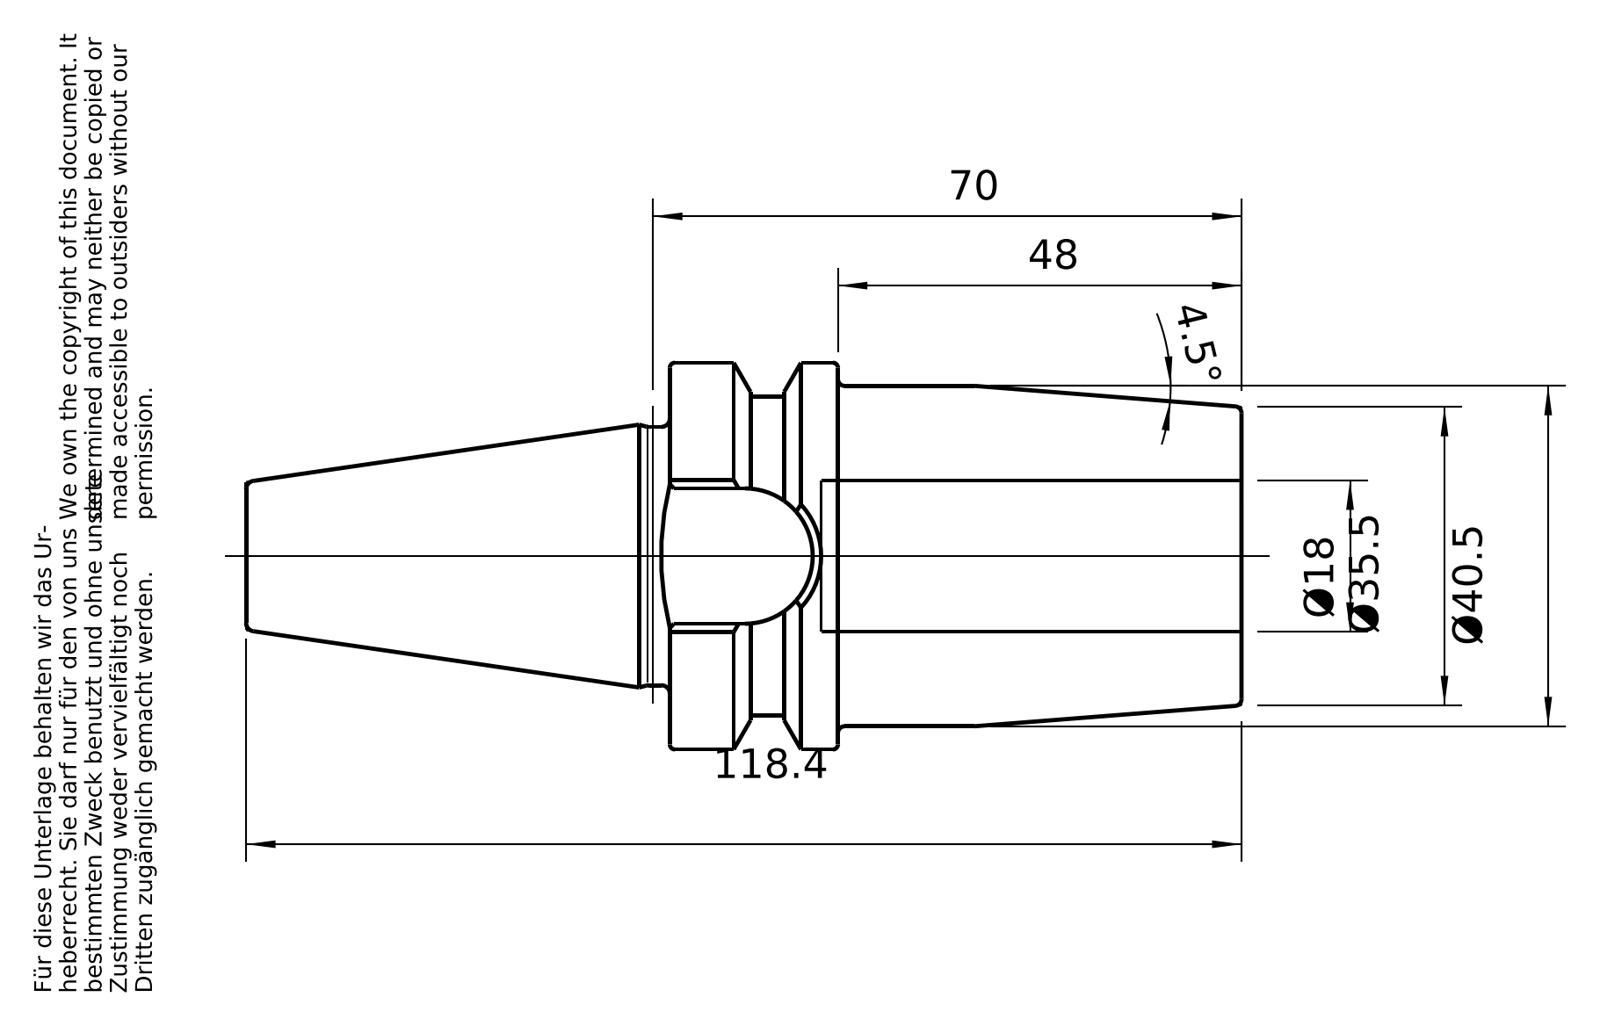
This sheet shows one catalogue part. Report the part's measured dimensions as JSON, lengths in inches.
{"part_name": "30-645-18", "step_written_by": "PRO/ENGINEER BY PARAMETRIC TECHNOLOGY CORPORATION, 2010430 (CONFIG_CONTROL_DESIGN)", "units": "inches", "bodies": {"solids": 1, "faces": 96, "planar": 26, "cylindrical": 22, "other": 48}, "overall_size": [4.661, 1.81, 1.81], "volume_in3": 5.723, "surface_area_in2": 31.25, "round_holes": [[0.398, 1], [0.493, 1], [0.512, 1], [0.709, 1]], "round_bosses_or_shafts": [[1.81, 1], [1.594, 1], [1.211, 1], [0.473, 1]], "partial_cylinders_radius": [[0.319, 1], [0.743, 1]], "face_to_face_distances": [2.677, 0.709, 1.969, 1.272, 0.787, 0.079, 1.89, 0.638, 1.984, 2.693]}
